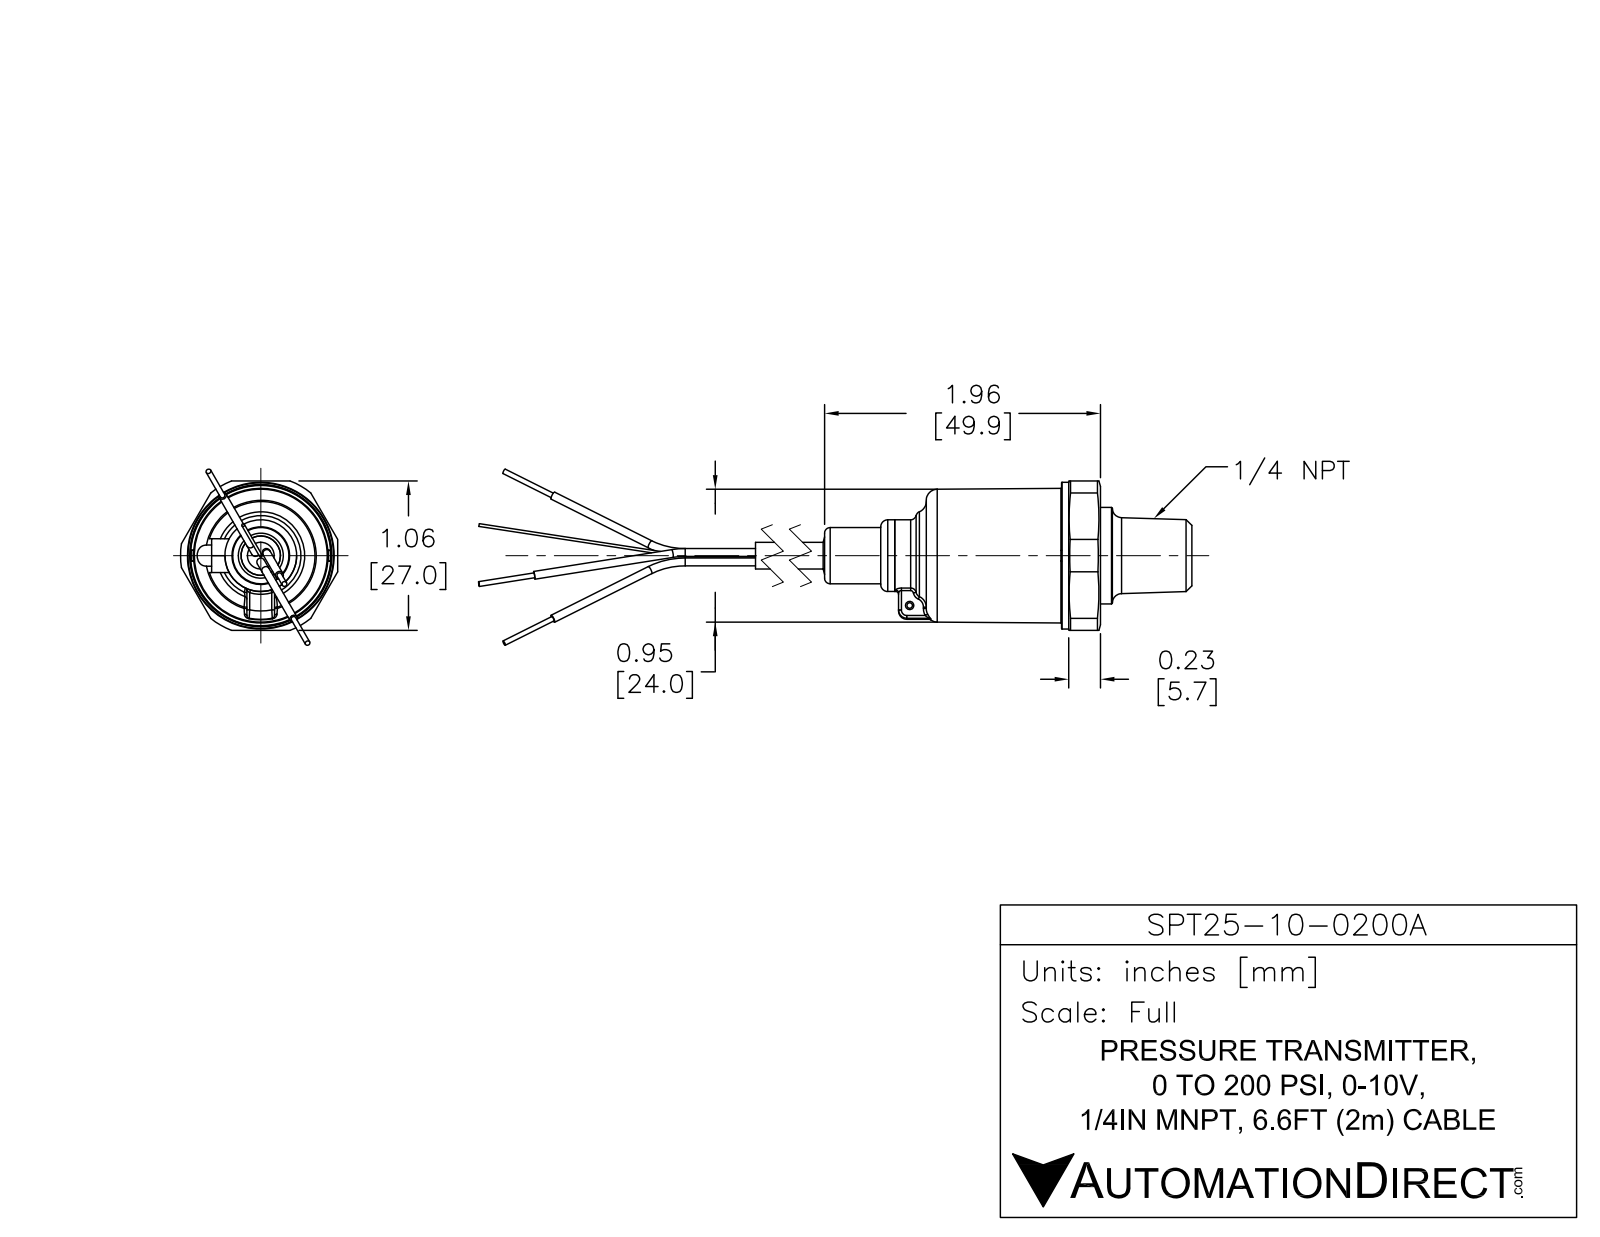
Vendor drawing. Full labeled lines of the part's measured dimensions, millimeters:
Part name (STEP PRODUCT): SPT25-10-0200A
STEP written by: SolidWorks 2017 (AUTOMOTIVE_DESIGN)
Units: millimetres
Bodies: 7 solids, 116 faces (32 planar, 49 cylindrical, 35 other)
Overall size (bounding box): 153.3 × 29 × 27.09
Volume: 20 801 mm³ · Surface area: 7 170 mm²
Round holes (diameter × count): ⌀1 ×1, ⌀3.3 ×1
Round bosses / shafts (diameter × count): ⌀1.4 ×6, ⌀0.75 ×5, ⌀26.75 ×1, ⌀24 ×1, ⌀17.5 ×1, ⌀14 ×1, ⌀13 ×1, ⌀10 ×1
Partial cylindrical surfaces — rounded edges, fillets, slot ends (radius × count): R2 ×1, R14.5 ×1
Main face-to-face distances: 6.75, 24, 17.25, 42.75, 49.5, 66.75, 44, 1.25, 5.5, 22.75
